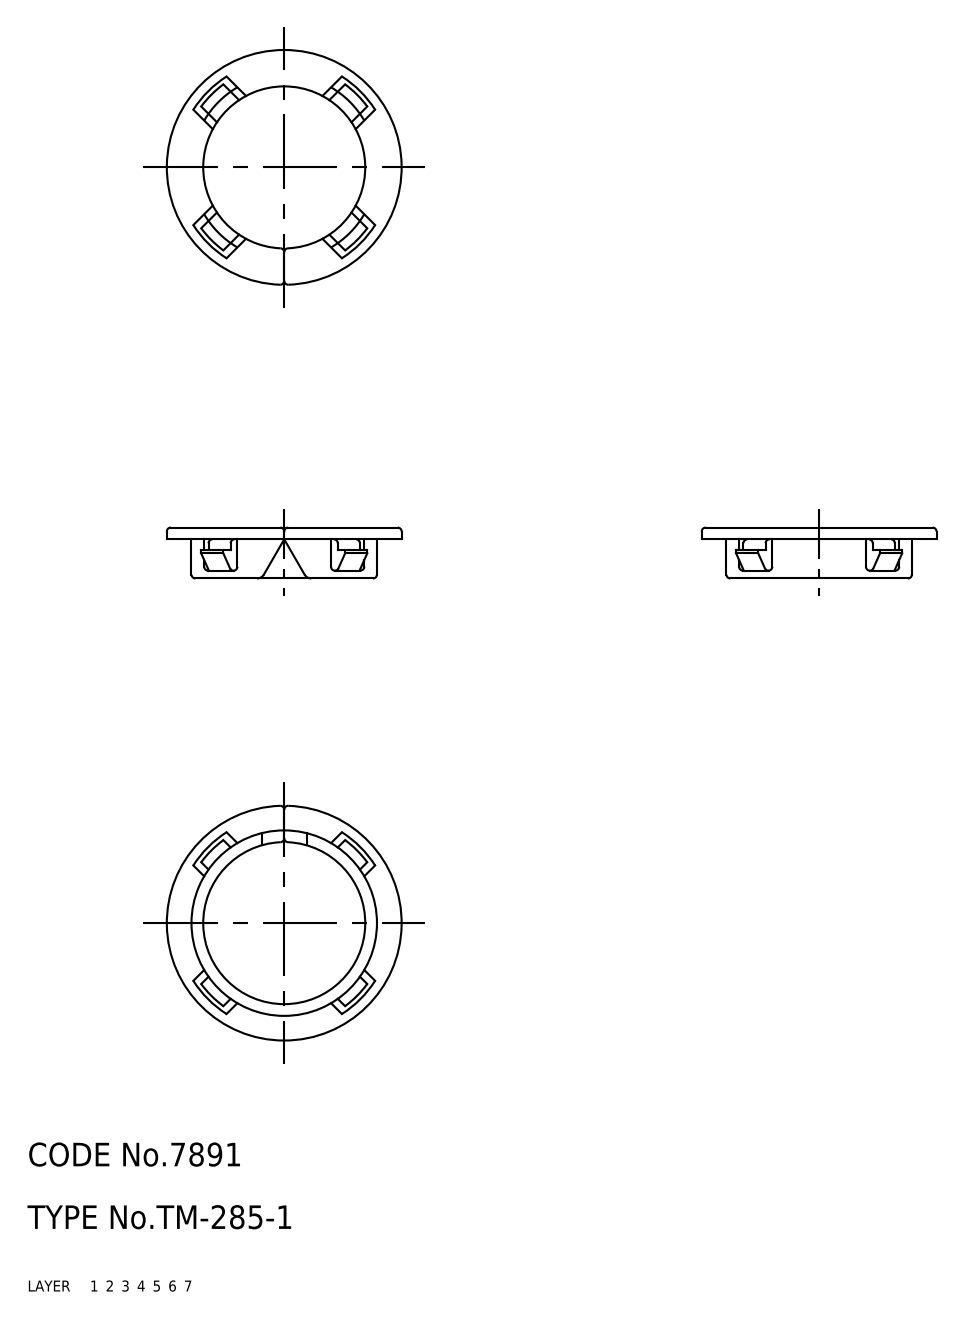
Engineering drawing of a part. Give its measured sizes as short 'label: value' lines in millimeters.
name: grommet
written by: CADfix (AUTOMOTIVE_DESIGN)
unit: mm
bodies: 1 solid, 82 faces (0 planar, 0 cylindrical, 82 other)
size: 30 × 29.99 × 6.5
volume: 891 mm³; area: 1 622 mm²
